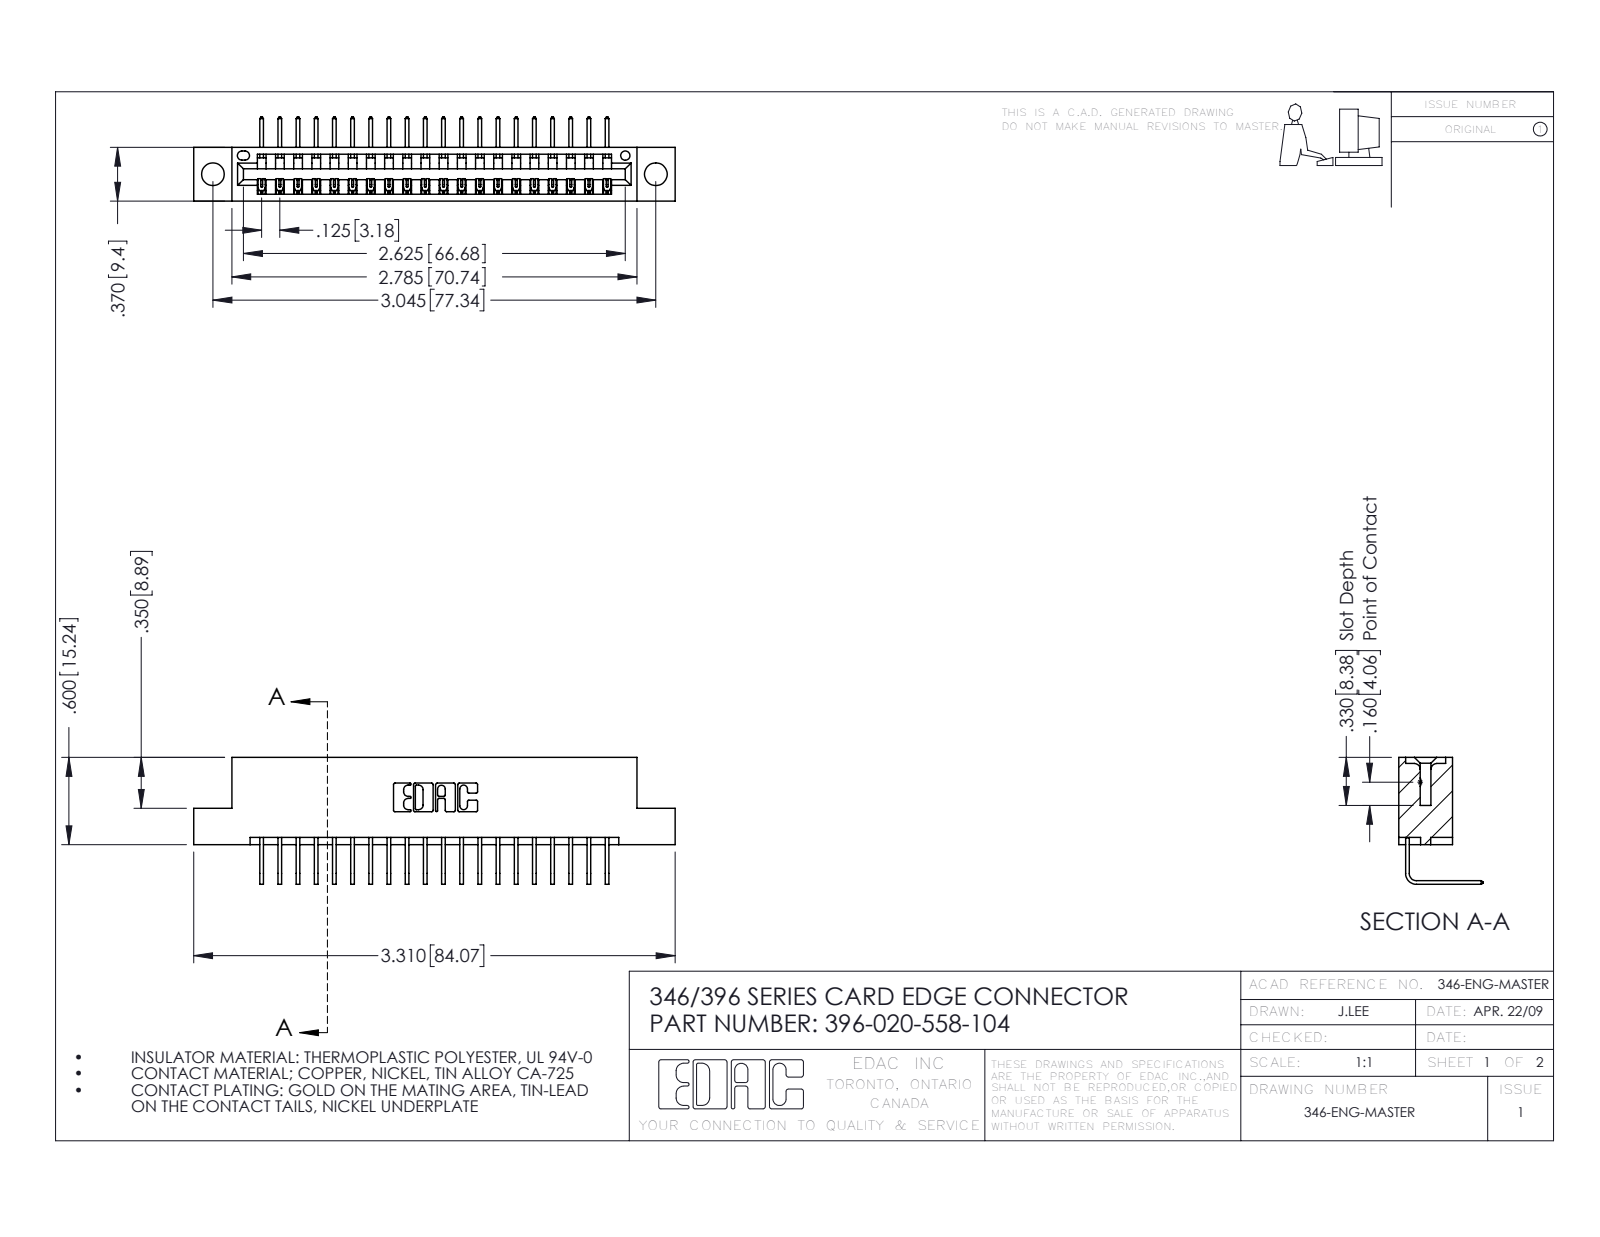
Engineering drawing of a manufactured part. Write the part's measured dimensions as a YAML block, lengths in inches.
part_name: "396-020-558-104; 346 Part_Flush Mounting Lugs - 0.156 Dia-TH; 345-292-001_558 Tail - 2"
step_written_by: "SolidWorks 2016 (CONFIG_CONTROL_DESIGN)"
units: inches
bodies: {solids: 21, faces: 1322, planar: 916, cylindrical: 406, other: 0}
overall_size: [3.31, 0.873, 0.58]
volume: 0.481
surface_area: 15.2
round_holes:
  - {diameter: 0.156, count: 2}
  - {diameter: 0.064, count: 1}
partial_cylinders:
  - {radius: 0.006, count: 40}
  - {radius: 0.01, count: 22}
  - {radius: 0.007, count: 6}
  - {radius: 0.031, count: 6}
  - {radius: 0.026, count: 3}
  - {radius: 0.031, count: 2}
  - {radius: 0.04, count: 2}
  - {radius: 0.014, count: 1}
face_to_face_distances: [0.322, 0.048, 0.37, 0.25, 0.298, 0.025, 0.072, 0.148, 0.222, 0.1]
hole_center_spacings: [0.246, 2.837, 3.045]
